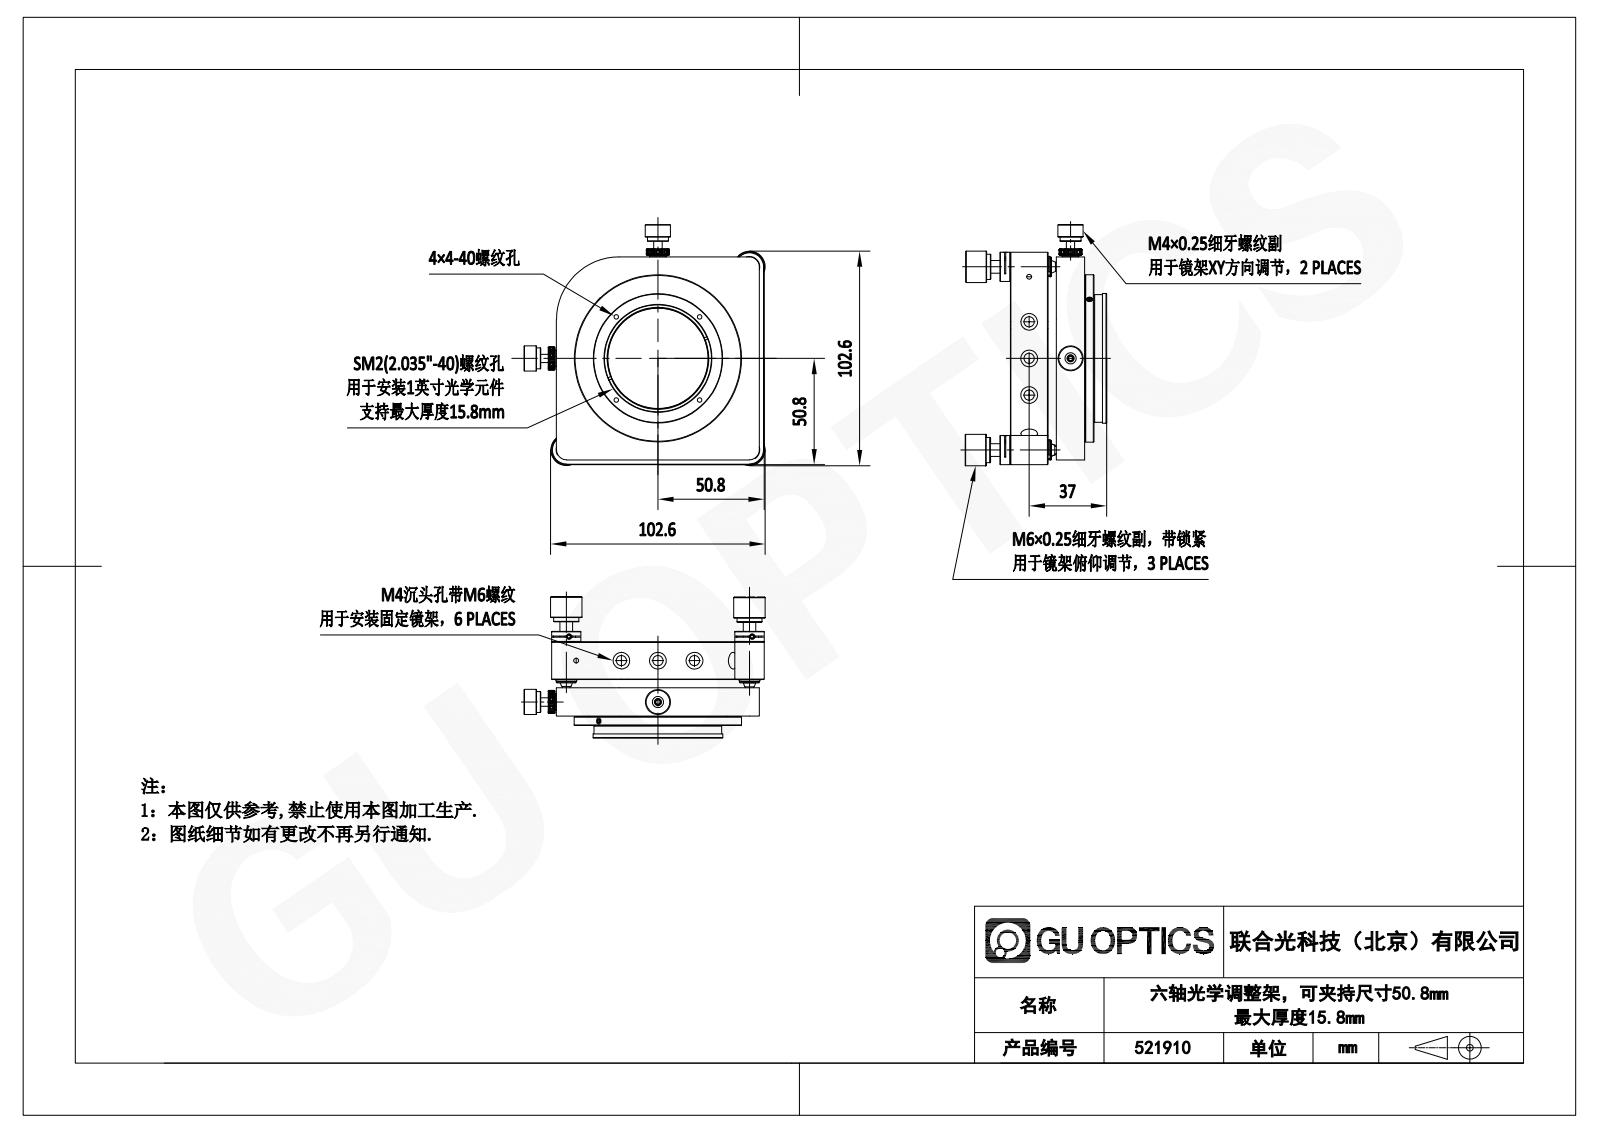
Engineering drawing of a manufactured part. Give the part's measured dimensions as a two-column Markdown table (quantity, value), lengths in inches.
| quantity | value |
| --- | --- |
| part name | 521910 |
| STEP written by | SolidWorks 2020 (CONFIG_CONTROL_DESIGN) |
| units | inches |
| bodies | 24 solids, 1506 faces (668 planar, 315 cylindrical, 523 other) |
| overall size | 4.539 × 4.539 × 2.661 |
| volume | 10.29 in³ |
| surface area | 94.77 in² |
| round holes (diameter × count) | 0.059 × 11, 0.098 × 7, 0.256 × 7, 0.197 × 6, 0.315 × 6, 0.157 × 5, 0.031 × 4, 0.089 × 4, 0.097 × 3, 0.157 × 3, 0.236 × 3, 0.138 × 2 |
| round bosses / shafts (diameter × count) | 0.472 × 5, 0.315 × 5, 0.118 × 4, 0.591 × 3, 0.551 × 3, 0.374 × 3, 0.394 × 2, 0.079 × 2 |
| partial cylindrical surfaces (radius × count) | 0.008 × 36, 0.041 × 8, 0.02 × 6, 0.157 × 3, 0.197 × 3, 0.217 × 2, 0.394 × 2, 1.181 × 1 |
| main face-to-face distances | 0.531, 0.866, 0.709, 0.089, 0.157, 1.398, 0.689, 1.575, 0.177, 3.823 |
| hole center spacings | 2.679, 0.122, 0.543, 0.689, 1.022, 1.039, 1.108, 1.567 |
